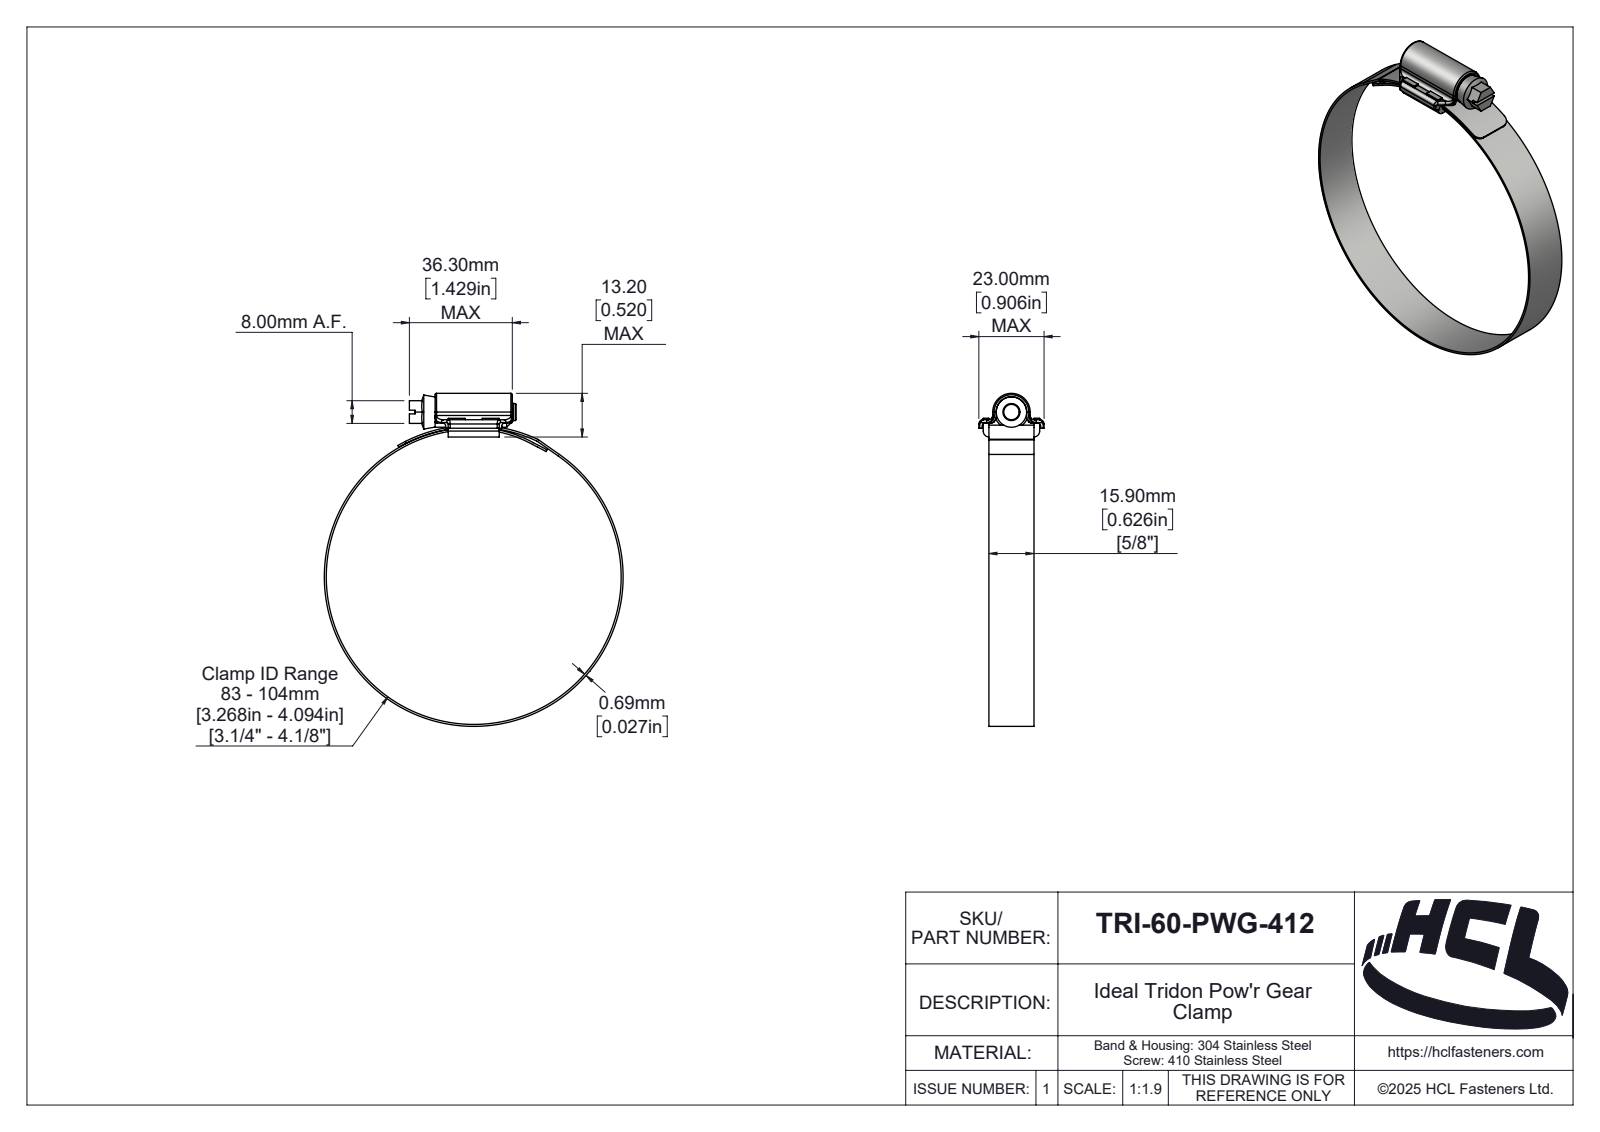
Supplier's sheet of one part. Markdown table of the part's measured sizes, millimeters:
| quantity | value |
| --- | --- |
| part name | TRI-60-PWG-412 |
| STEP written by | SolidWorks 2025 (AUTOMOTIVE_DESIGN) |
| units | millimeters |
| bodies | 4 solids, 268 faces (87 planar, 102 cylindrical, 79 other) |
| overall size | 117.39 × 105.38 × 23 |
| volume | 9 408 mm³ |
| surface area | 17 353 mm² |
| round holes (diameter × count) | 104 × 1 |
| round bosses / shafts (diameter × count) | 105.38 × 1, 10.7 × 1, 6 × 1 |
| partial cylindrical surfaces (radius × count) | 1 × 14, 0.5 × 4, 1.5 × 4, 2 × 3, 0.1 × 2, 2.1 × 2, 3 × 2, 0.46 × 1 |
| main face-to-face distances | 2, 15.9, 17.9, 4.9, 0.69, 1.2, 4.55, 3.35, 15.35, 2.55 |
